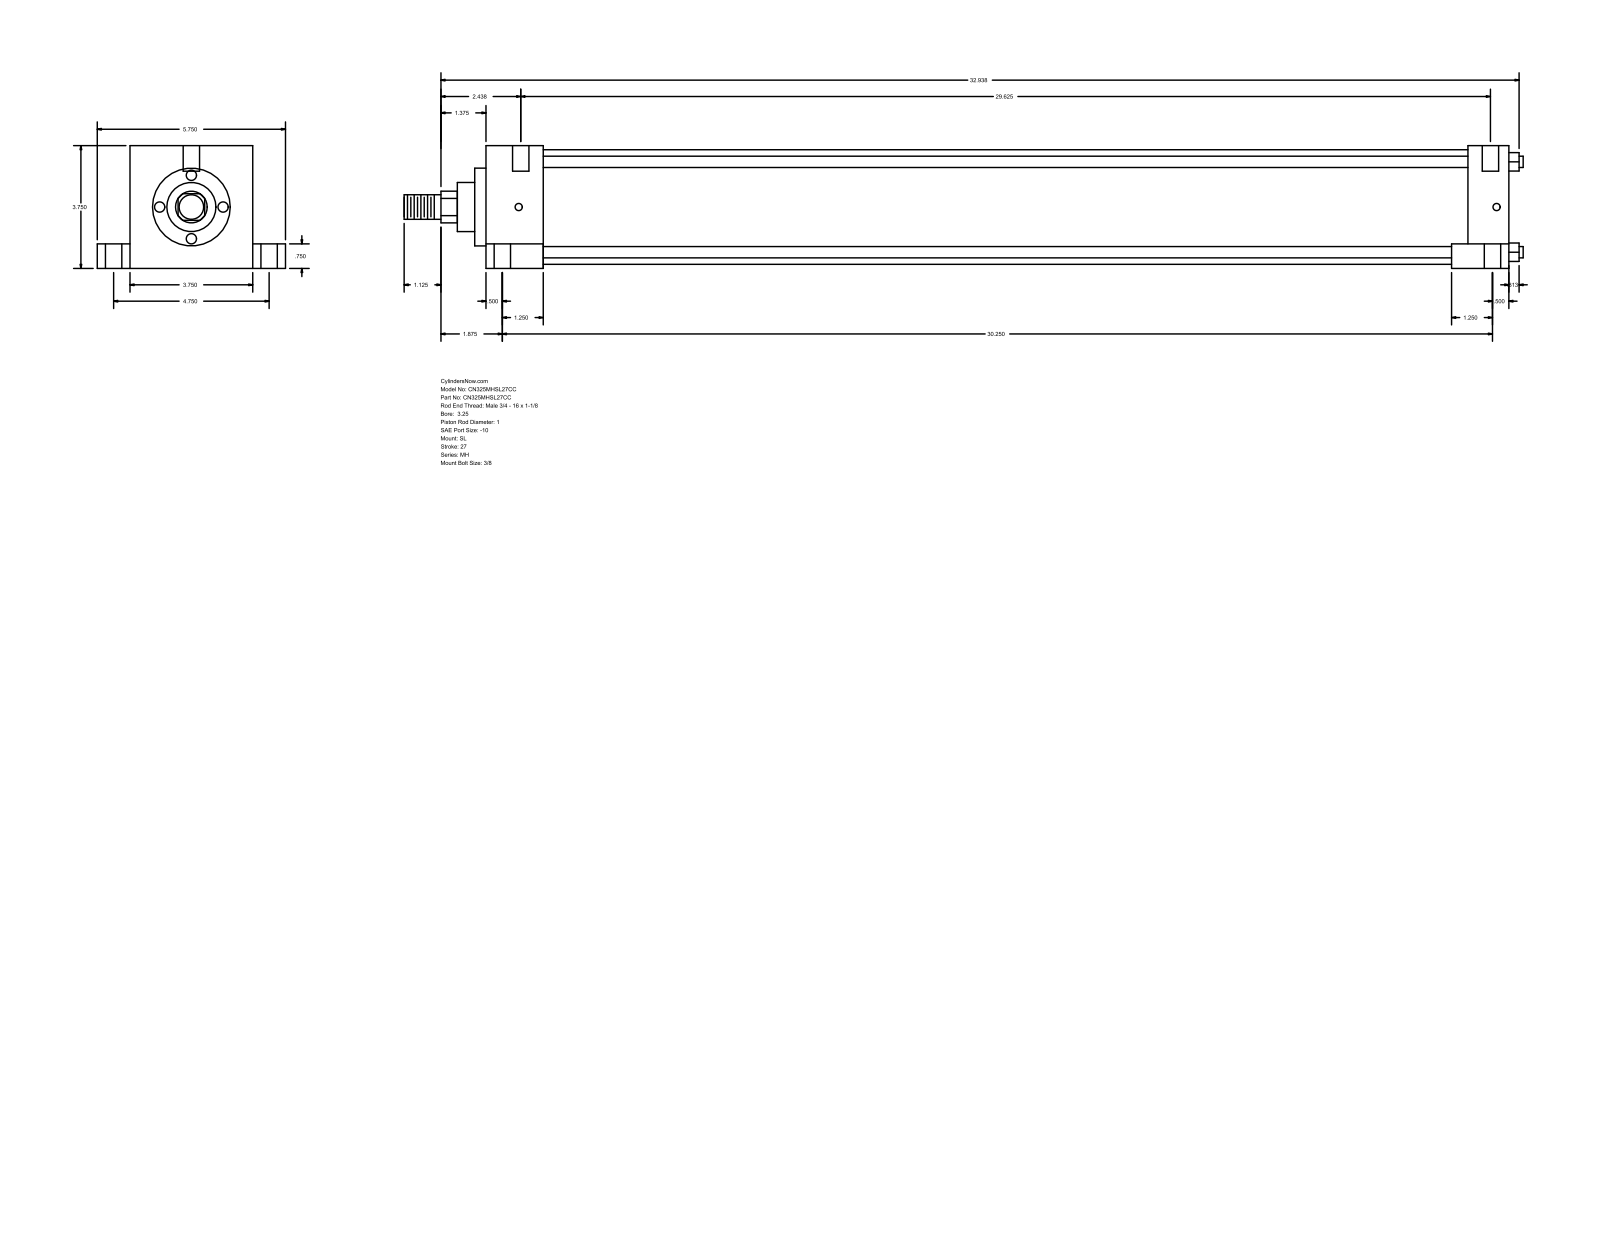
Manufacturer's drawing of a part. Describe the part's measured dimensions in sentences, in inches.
The part is named "MH_SL__0325_1". Its 3-D file was written by "GSSL Pune (CONFIG_CONTROL_DESIGN)". It is 0 solids with 110 faces: 77 planar, 33 cylindrical and 0 other. Overall it measures 34.187 by 5.75 by 3.75 inches. Round holes: 6 of diameter 0.5, 4 of diameter 0.219, 4 of diameter 0.75. Round bosses or shafts: 4 of diameter 0.345, 1 of diameter 3.5, 1 of diameter 2.375, 1 of diameter 1.5, 1 of diameter 1, 1 of diameter 0.75. Partial cylindrical surfaces (rounded edges, fillets, slot ends): 1 of radius 0.484. The main face-to-face distances are 3.75, 31.25, 1.75, 29.5, 1, 4.75, 0.75, 3, 30, 28.25. The hole center spacings are 2.376, 2.378, 2.427, 2.441, 4.75, 29.783, 29.844, 29.875.
